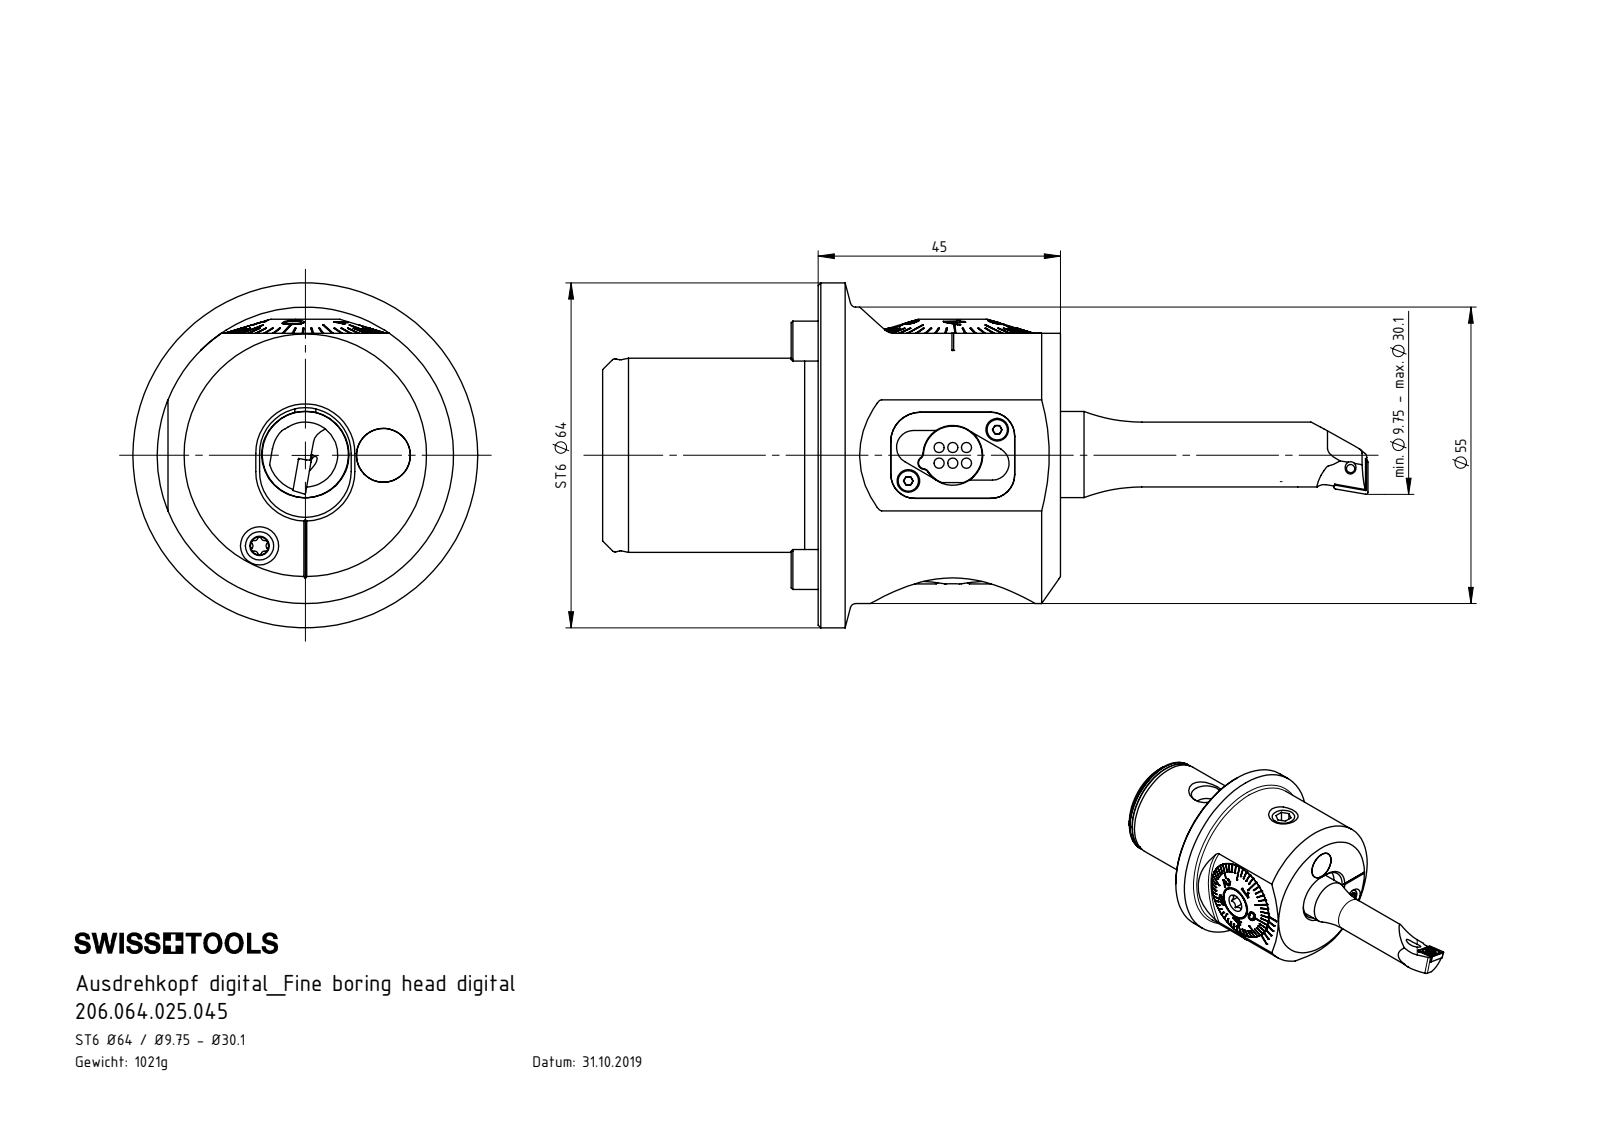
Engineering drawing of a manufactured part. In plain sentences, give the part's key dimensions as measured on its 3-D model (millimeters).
The part is named "A55-BG1.DA2.041_Dichtung; PEF-DA1.011.017_A; DIN 3771 - 25x1.5; Fxx-BG7.DA1.0xx_B_F42 (+8 more)". Its 3-D file was written by "SolidWorks 2017 (AUTOMOTIVE_DESIGN)". It is 26 solids with 814 faces: 426 planar, 170 cylindrical and 218 other. Overall it measures 85 by 64 by 64 millimeters. Its volume is 124 773 cubic millimeters and its surface area 47 710 square millimeters. Round holes: 4 of diameter 3.2, 4 of diameter 8.5, 3 of diameter 1.6, 3 of diameter 4.2, 2 of diameter 2.2, 2 of diameter 5, 1 of diameter 3.3, 1 of diameter 8, 1 of diameter 10, 1 of diameter 10.1, 1 of diameter 11.1, 1 of diameter 11.75. Round bosses or shafts: 6 of diameter 1.9, 3 of diameter 10, 2 of diameter 3.8, 2 of diameter 2, 1 of diameter 64, 1 of diameter 55, 1 of diameter 36, 1 of diameter 35.8. Partial cylindrical surfaces (rounded edges, fillets, slot ends): 6 of radius 0.34, 6 of radius 0.59, 6 of radius 1.1, 6 of radius 1.2, 4 of radius 0.5, 4 of radius 4.5, 3 of radius 3.2, 3 of radius 4.4. The main face-to-face distances are 45, 5.65, 4, 5.3, 3.15, 2.5, 2.8, 0.35, 6.51, 40. The hole center spacings are 4.1, 4.33, 7.25, 8.44, 9.52, 12, 12.68, 14.5.
